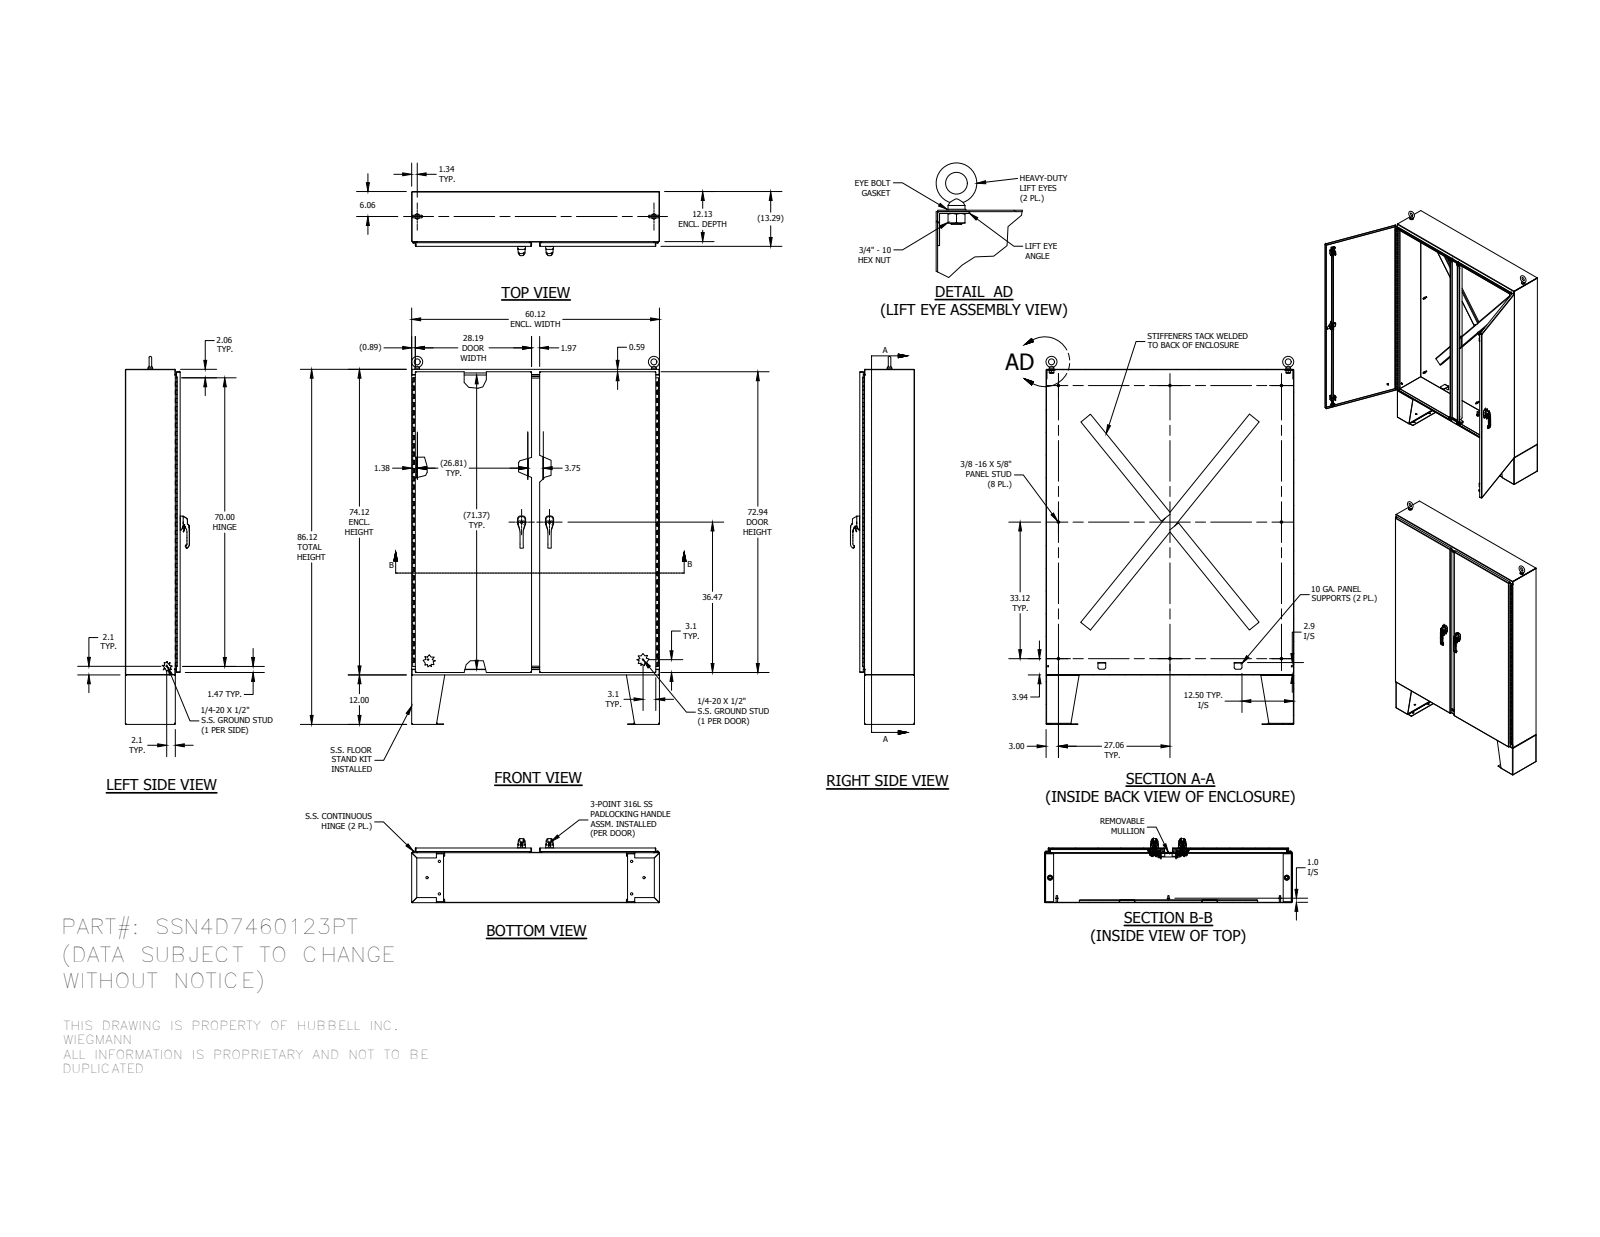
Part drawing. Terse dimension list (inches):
name: LOCK-NUT_AF0_1; HFW32451_1; 328131-70_1; SSN4D74603PTRDR_1 (+8 more)
written by: SolidWorks 2014 (AUTOMOTIVE_DESIGN)
unit: in
bodies: 138 solids, 7352 faces (2804 planar, 2832 cylindrical, 1716 other)
size: 89.248 × 60.125 × 15.538
volume: 1 516 in³; area: 31 889 in²
holes: 18× ⌀0.563, 16× ⌀0.262, 16× ⌀0.375, 8× ⌀0.187, 6× ⌀0.213, 6× ⌀0.281, 5× ⌀0.25, 4× ⌀0.196, 4× ⌀0.241, 4× ⌀0.252, 4× ⌀0.281, 4× ⌀0.315
bosses: 10× ⌀0.33, 8× ⌀0.625, 7× ⌀0.25, 6× ⌀0.533, 6× ⌀0.236, 5× ⌀1, 4× ⌀0.563, 4× ⌀0.531
rounds: 352× R0.02, 213× R0.012, 46× R0.125, 44× R0.019, 34× R0.05, 32× R0.031, 28× R0.079, 24× R0.025
face distances: 0.094, 13.193, 13.196, 13.1, 13.102, 13.287, 0.091, 13.29, 0.096, 60.031
hole spacings: 15.556, 0.38, 0.38, 0.76, 7.778, 31.111, 58.326, 64.052
